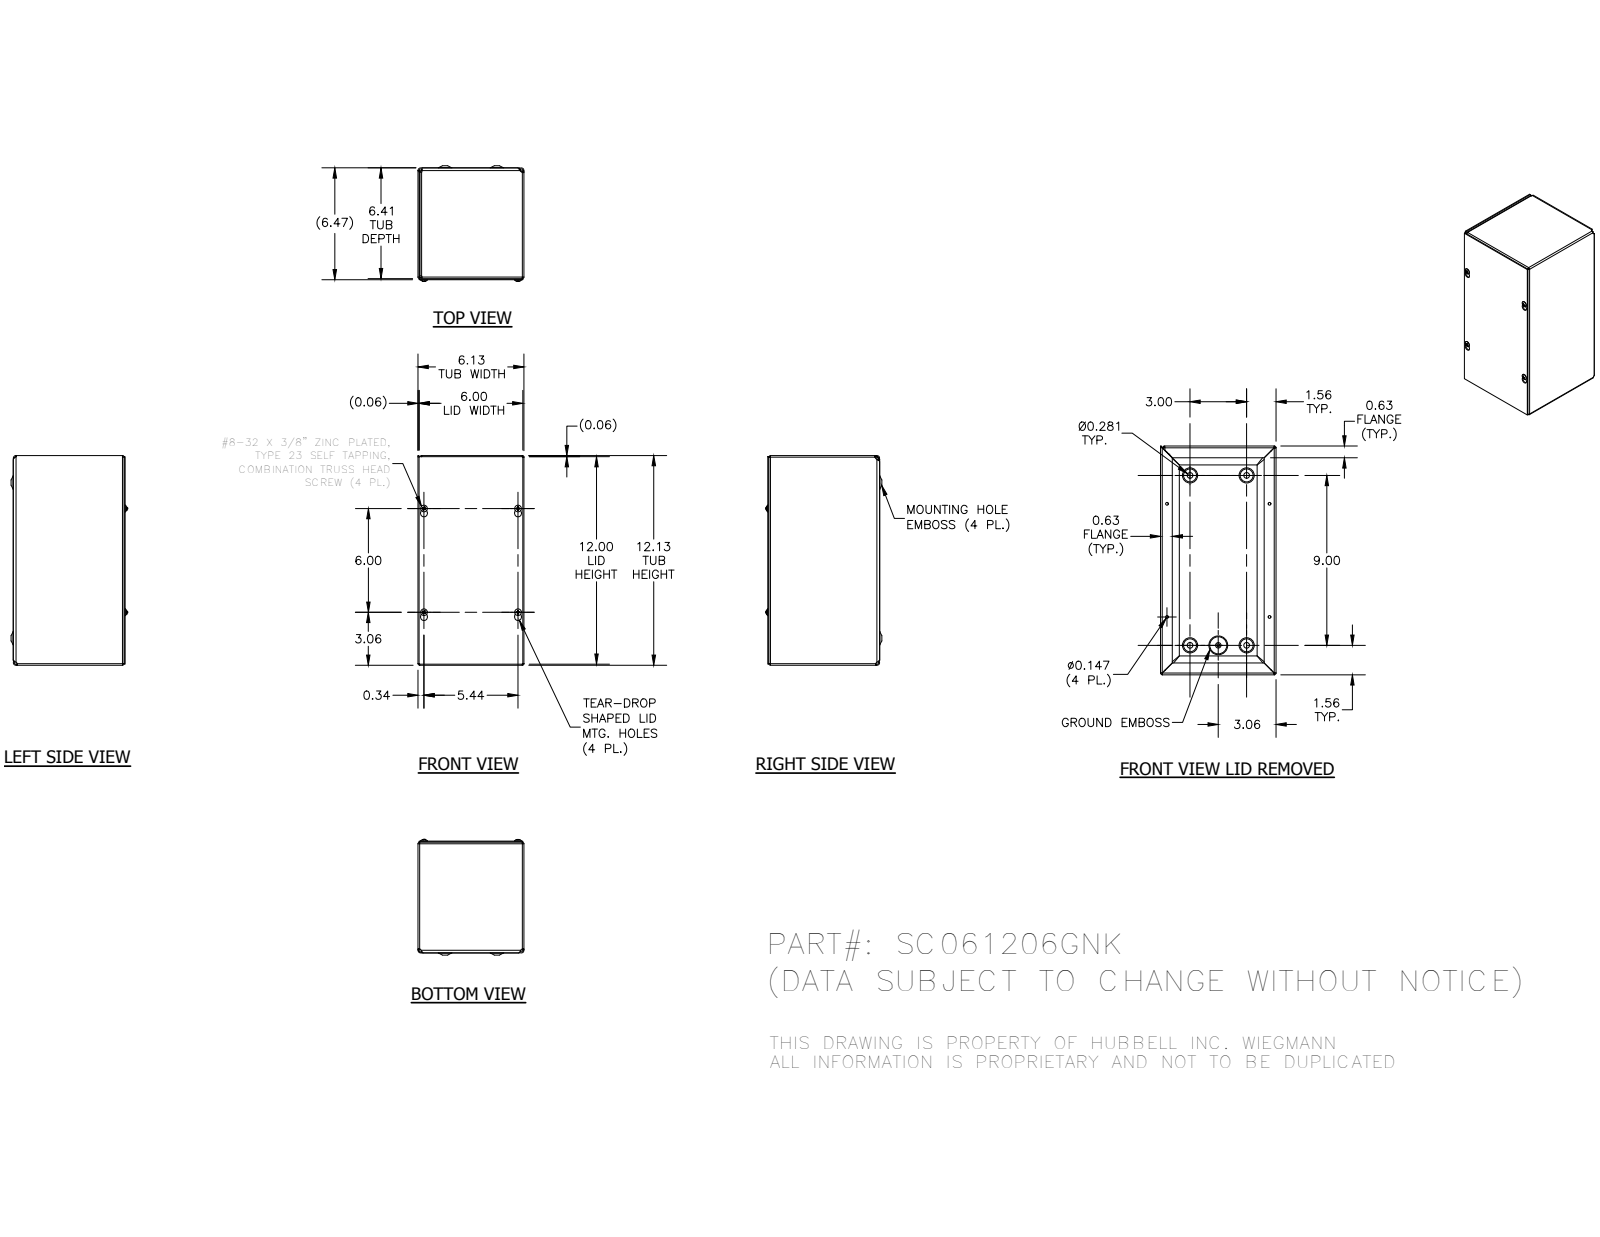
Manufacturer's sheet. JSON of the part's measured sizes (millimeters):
{"part_name": "SC0612GNKBKP; SC061206GNKWRA; SC0612GNKLID; 34056 (+1 more)", "step_written_by": "Autodesk Inventor 2014 (AUTOMOTIVE_DESIGN)", "units": "millimeters", "bodies": {"solids": 7, "faces": 358, "planar": 133, "cylindrical": 73, "other": 152}, "overall_size": [307.98, 170, 155.57], "volume_mm3": 425798, "surface_area_mm2": 547624, "round_holes": [[3.73, 4], [7.62, 4], [4.19, 1]], "round_bosses_or_shafts": [[9.75, 4], [4.17, 4], [5.8, 1]], "partial_cylinders_radius": [[0.79, 8], [2.37, 8], [1.4, 4], [1.57, 4], [2.38, 4], [2.97, 4], [3.15, 4], [3.17, 4]], "face_to_face_distances": [1.57, 154, 161.12, 152.43, 155.57, 306.4, 162.69, 1.59, 162.71, 164.28], "hole_center_spacings": [38.1, 76.2, 113.72, 138.11, 152.4, 192.98, 193.02, 202.61]}
